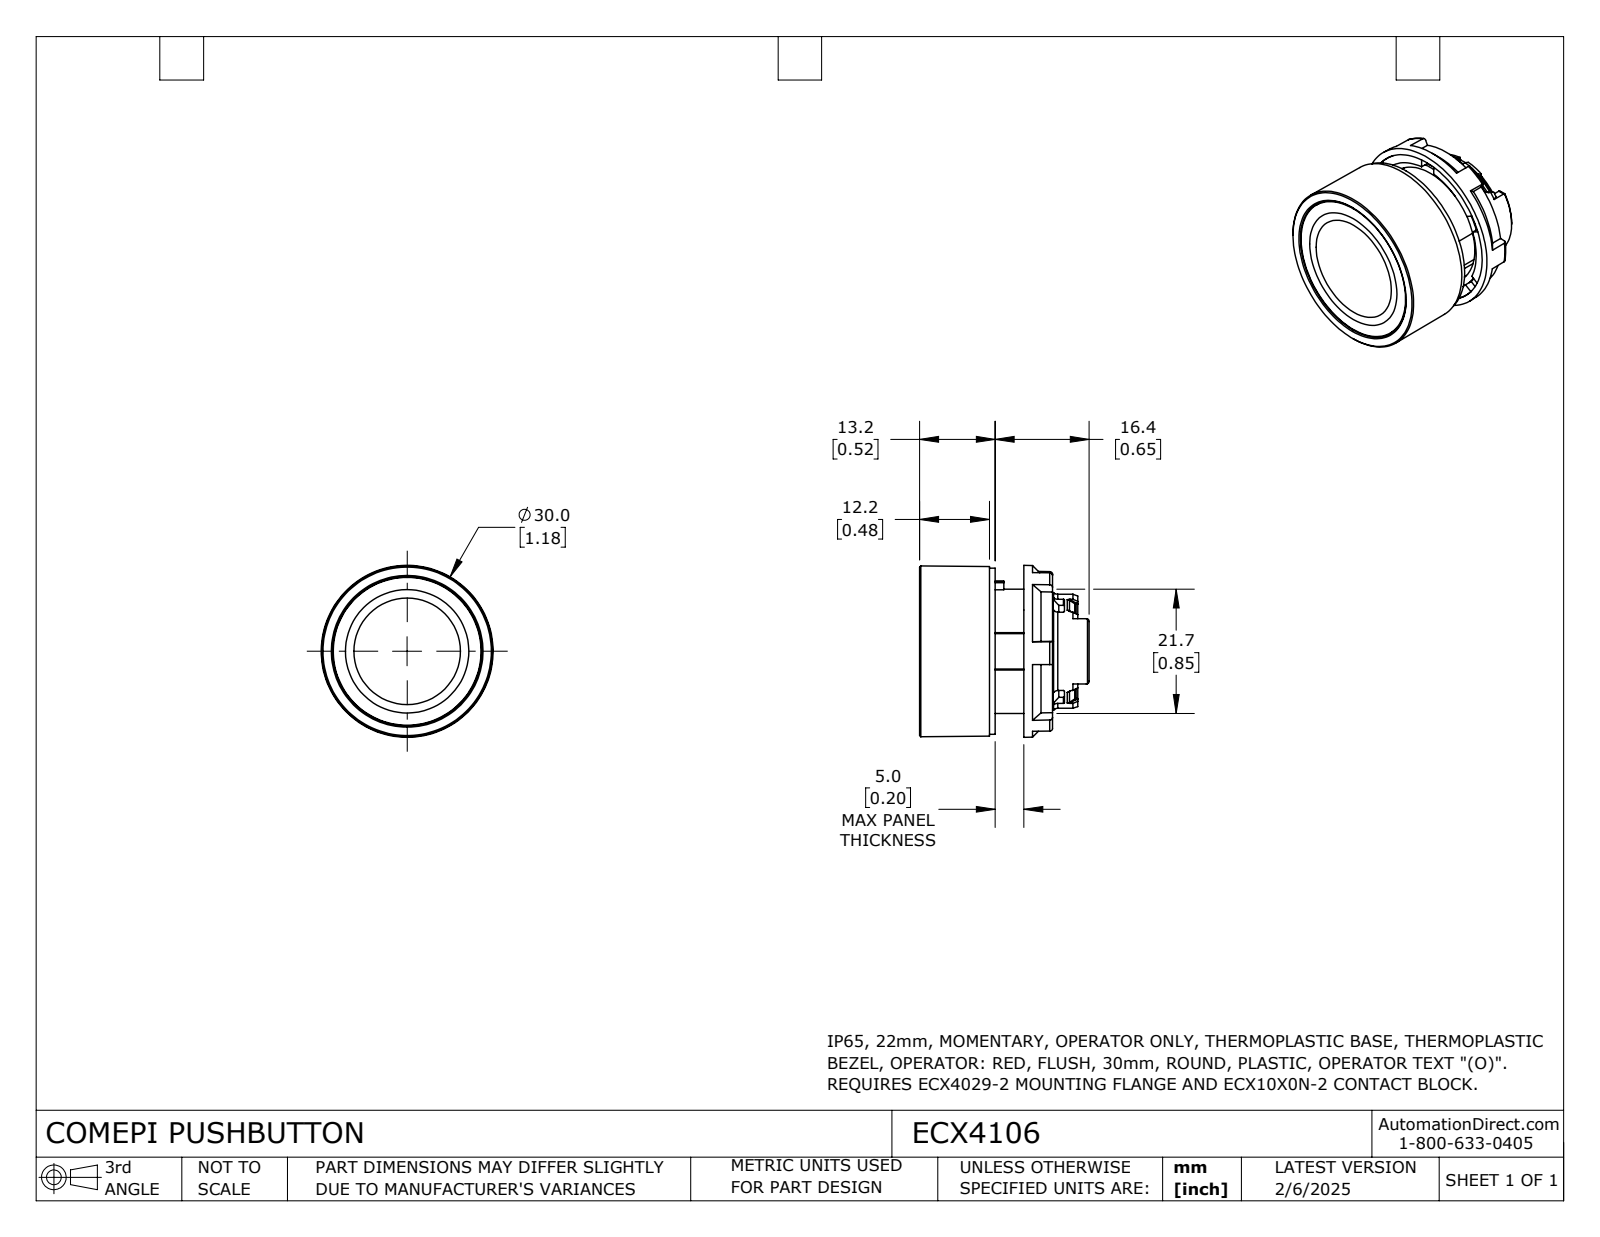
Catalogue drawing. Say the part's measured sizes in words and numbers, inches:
The part is named "ECX4106". Its 3-D file was written by "SolidWorks 2024 (CONFIG_CONTROL_DESIGN)". It is 3 solids with 398 faces: 134 planar, 111 cylindrical and 153 other. Overall it measures 1.181 by 1.181 by 1.165 inches. Its volume is 0.472 cubic inches and its surface area 16.55 square inches. Round holes: 1 of diameter 0.531, 1 of diameter 0.713, 1 of diameter 0.866. Round bosses or shafts: 1 of diameter 1.142, 1 of diameter 1.016, 1 of diameter 0.965, 1 of diameter 0.854, 1 of diameter 0.807, 1 of diameter 0.787, 1 of diameter 0.748, 1 of diameter 0.728. Partial cylindrical surfaces (rounded edges, fillets, slot ends): 24 of radius 0.008, 8 of radius 0.02, 2 of radius 0.01, 1 of radius 0.293, 1 of radius 0.344, 1 of radius 0.348, 1 of radius 0.366. The main face-to-face distances are 0.409, 0.039, 0.433, 0.472, 0.236, 0.394, 0.197, 0.449, 0.512, 0.217.
